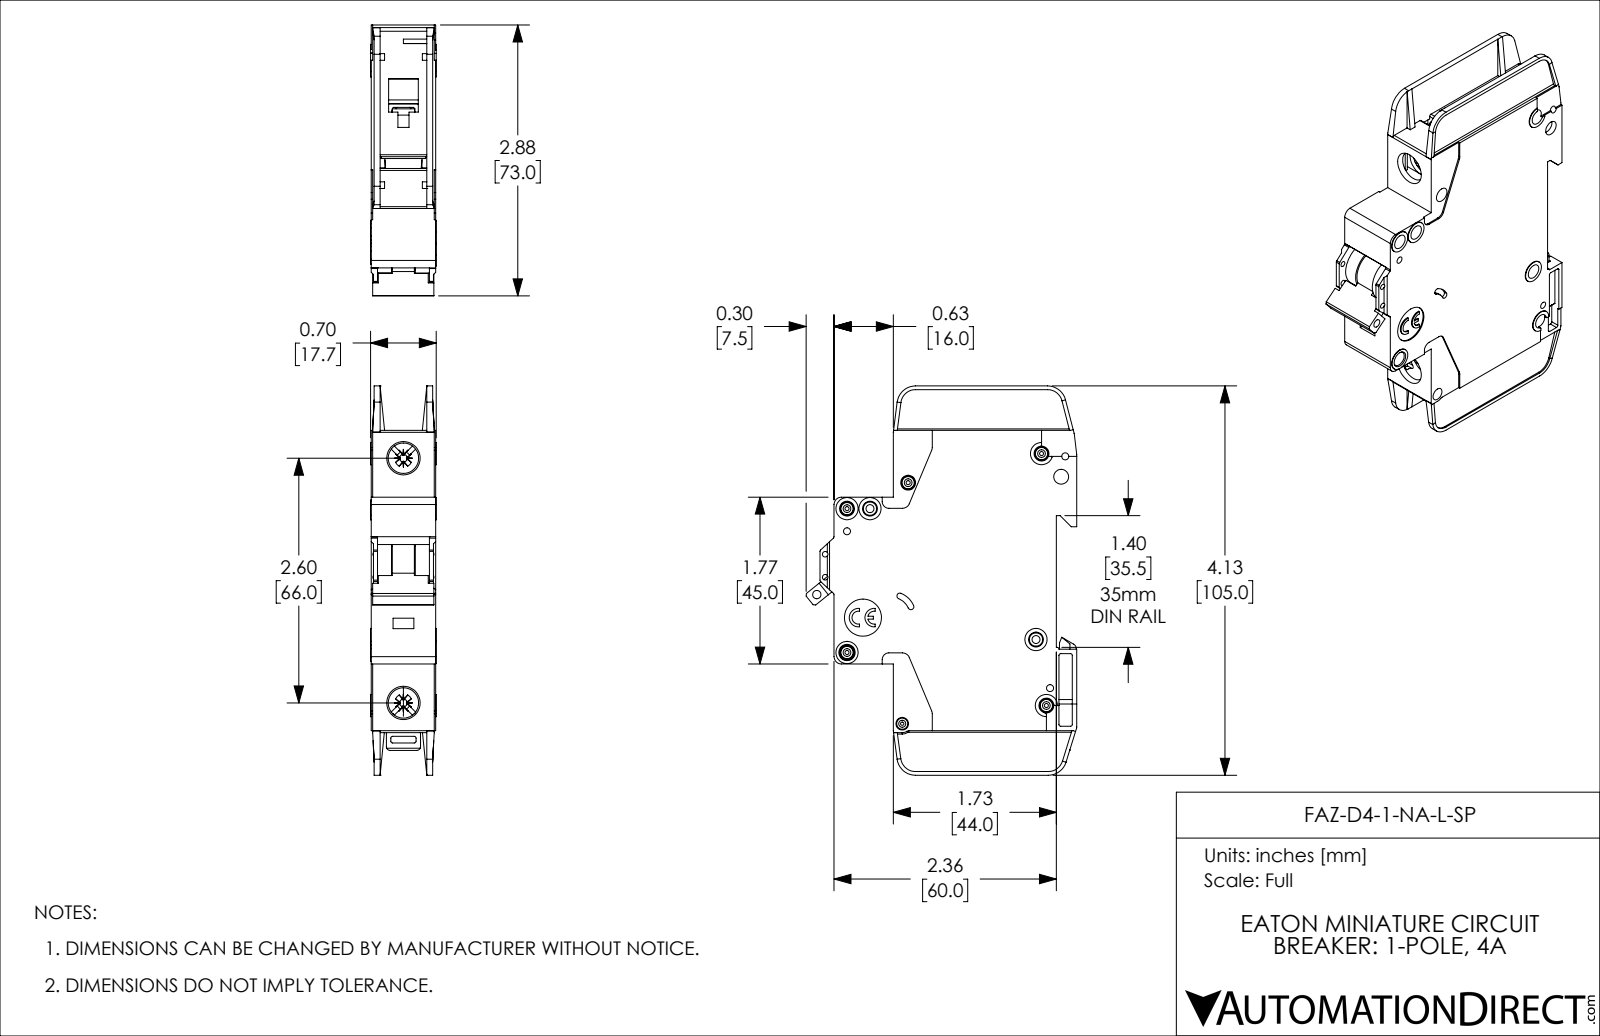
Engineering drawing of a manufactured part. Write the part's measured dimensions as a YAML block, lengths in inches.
part_name: "FAZ-D4-1-NA-L-SP"
step_written_by: "SolidWorks 2019 (AUTOMOTIVE_DESIGN)"
units: inches
bodies: {solids: 1, faces: 1127, planar: 671, cylindrical: 357, other: 99}
overall_size: [4.134, 2.876, 0.697]
volume: 4.682
surface_area: 41.01
round_holes:
  - {diameter: 0.157, count: 8}
  - {diameter: 0.043, count: 5}
  - {diameter: 0.075, count: 4}
  - {diameter: 0.059, count: 2}
  - {diameter: 0.085, count: 2}
  - {diameter: 0.323, count: 2}
  - {diameter: 0.035, count: 1}
  - {diameter: 0.089, count: 1}
  - {diameter: 0.098, count: 1}
  - {diameter: 0.134, count: 1}
  - {diameter: 0.394, count: 1}
round_bosses_or_shafts:
  - {diameter: 0.13, count: 5}
  - {diameter: 0.236, count: 4}
  - {diameter: 0.118, count: 2}
  - {diameter: 0.098, count: 1}
partial_cylinders:
  - {radius: 0.02, count: 42}
  - {radius: 0.016, count: 10}
  - {radius: 0.039, count: 10}
  - {radius: 0.079, count: 8}
  - {radius: 0.197, count: 5}
  - {radius: 0.008, count: 4}
  - {radius: 0.026, count: 4}
  - {radius: 0.043, count: 4}
face_to_face_distances: [0.047, 0.685, 0.591, 0.638, 0.094, 0.543, 0.016, 0.031, 0.496, 0.575]
hole_center_spacings: [0.244, 0.537, 0.87, 0.189, 0.199, 0.204, 0.221, 0.24]
